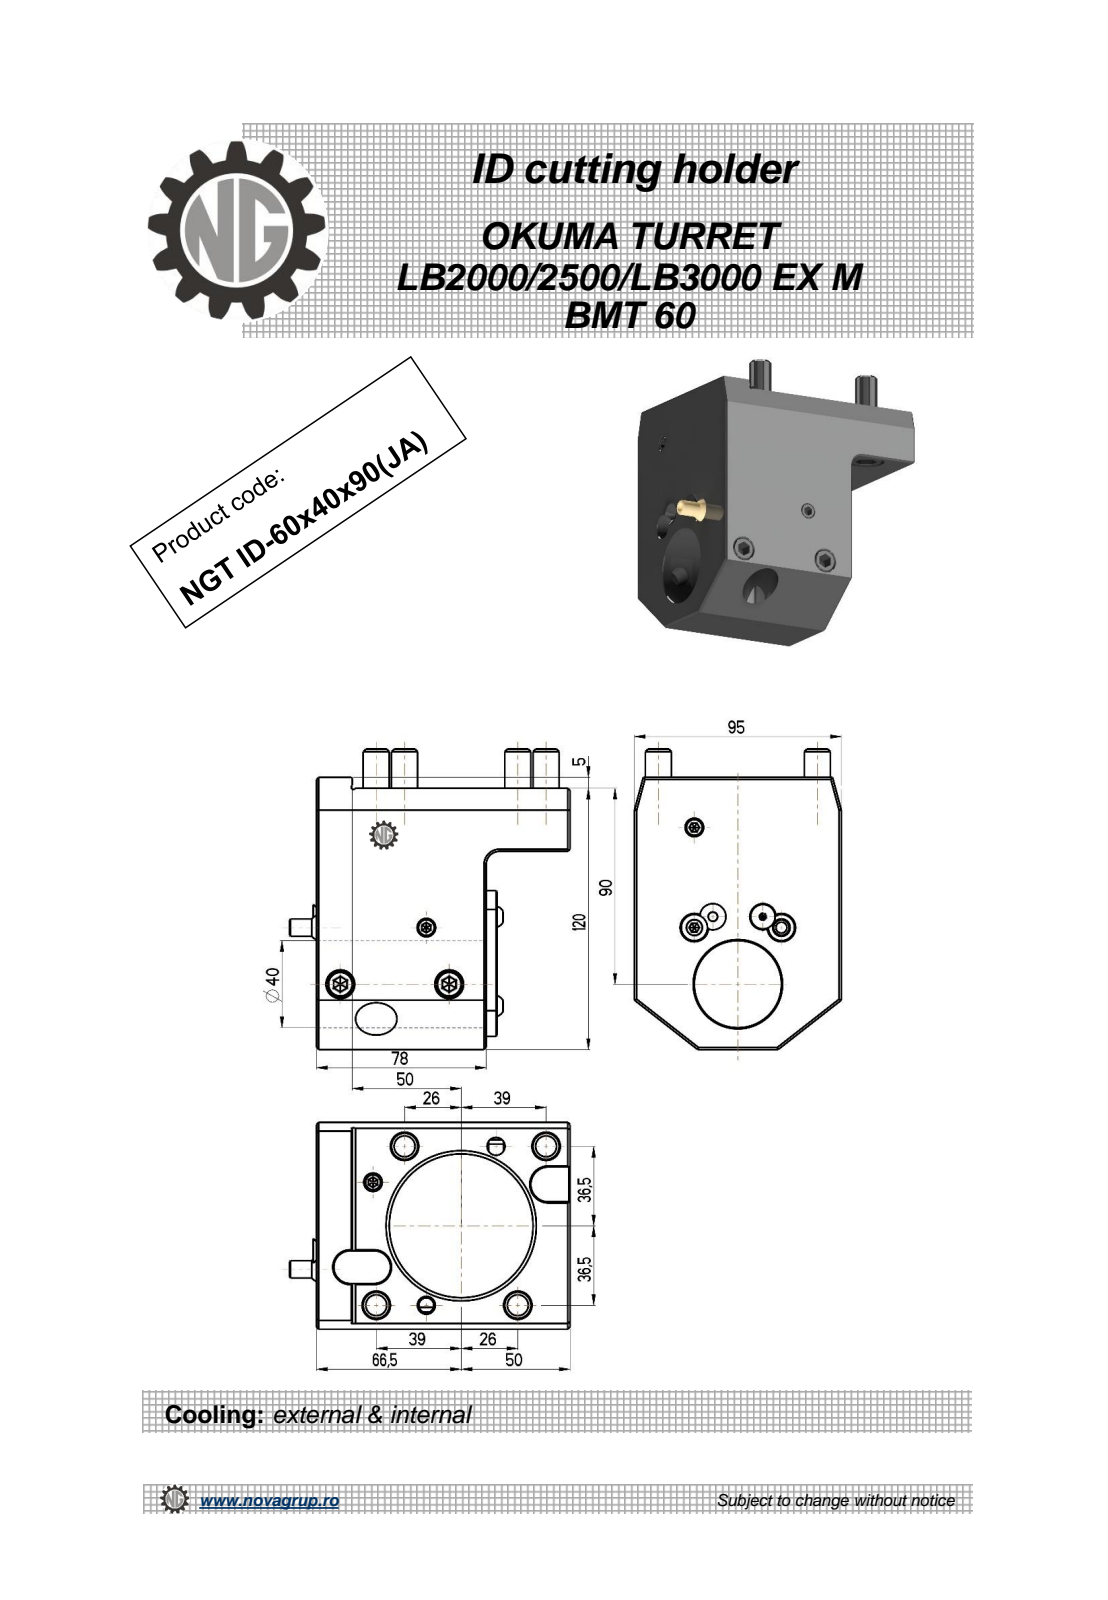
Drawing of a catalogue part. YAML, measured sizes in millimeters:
part_name: "NGT_ID_60_40_90_JA"
step_written_by: "PRO/ENGINEER BY PARAMETRIC TECHNOLOGY CORPORATION, 2010280 (CONFIG_CONTROL_DESIGN)"
units: millimeters
bodies: {solids: 1, faces: 332, planar: 171, cylindrical: 70, other: 91}
overall_size: [138, 128.87, 95]
volume: 864469
surface_area: 82852
round_holes:
  - {diameter: 8.2, count: 2}
  - {diameter: 10.2, count: 2}
  - {diameter: 5, count: 1}
  - {diameter: 6.8, count: 1}
  - {diameter: 40, count: 1}
  - {diameter: 69, count: 1}
round_bosses_or_shafts:
  - {diameter: 12, count: 4}
  - {diameter: 61, count: 1}
  - {diameter: 11.2, count: 1}
  - {diameter: 8, count: 1}
partial_cylinders:
  - {radius: 0.61, count: 24}
  - {radius: 0.22, count: 6}
  - {radius: 7.5, count: 2}
  - {radius: 1, count: 1}
  - {radius: 4, count: 1}
  - {radius: 6, count: 1}
  - {radius: 8, count: 1}
face_to_face_distances: [95, 78, 5, 83, 29, 91, 120, 38.5, 33.5, 116.5]
hole_center_spacings: [39.85, 32.8, 50, 79.71]
